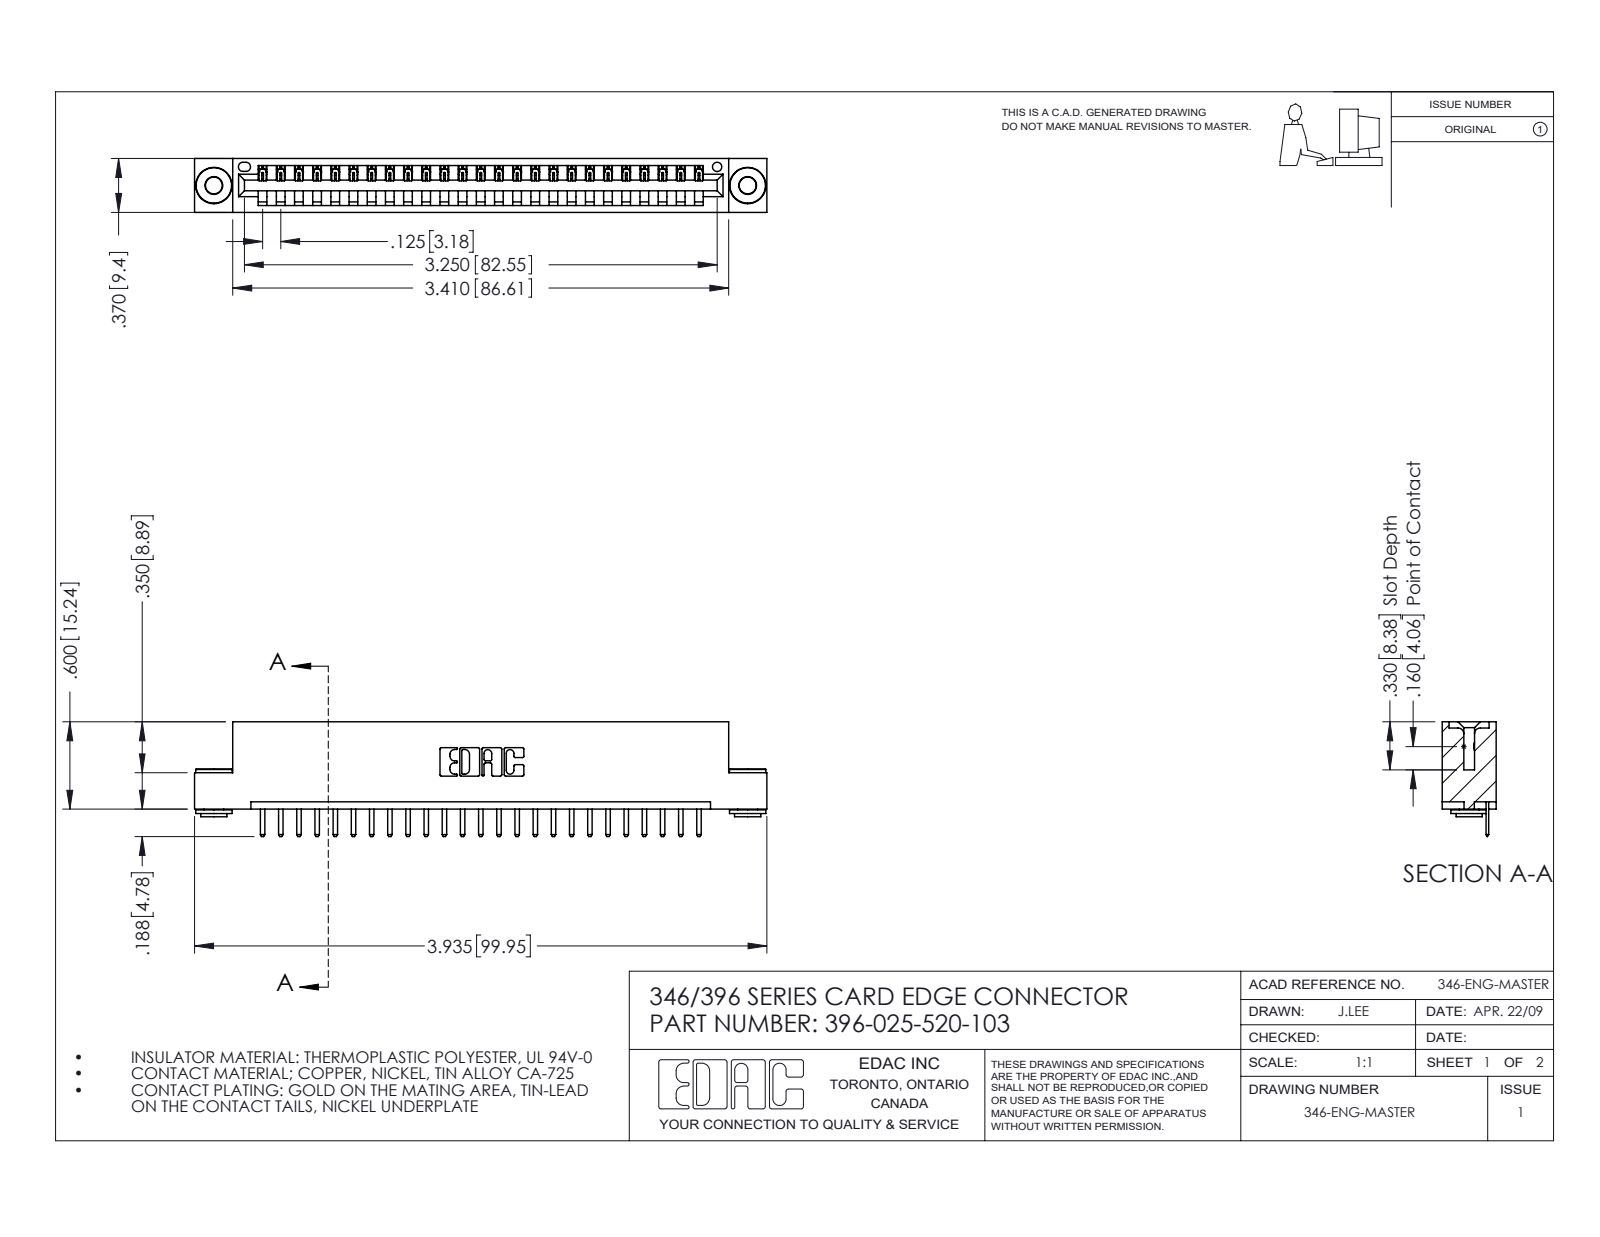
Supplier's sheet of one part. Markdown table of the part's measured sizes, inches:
| quantity | value |
| --- | --- |
| part name | 345-250-002_345-250-002-102; 396-025-520-103; 346 Part_Flush Mounting Lugs - 0.156 Dia-TH; 345-292-001_345-293-120 |
| STEP written by | SolidWorks 2016 (CONFIG_CONTROL_DESIGN) |
| units | inches |
| bodies | 28 solids, 1710 faces (1136 planar, 566 cylindrical, 8 other) |
| overall size | 3.935 × 0.788 × 0.37 |
| volume | 0.573 in³ |
| surface area | 17.89 in² |
| round holes (diameter × count) | 0.116 × 2, 0.156 × 2, 0.064 × 1 |
| round bosses / shafts (diameter × count) | 0.25 × 2, 0.18 × 2, 0.136 × 2 |
| partial cylindrical surfaces (radius × count) | 0.01 × 52, 0.006 × 50, 0.01 × 22, 0.007 × 6, 0.031 × 6, 0.026 × 3, 0.031 × 2, 0.04 × 2 |
| main face-to-face distances | 0.048, 0.322, 0.37, 0.25, 0.148, 0.222, 0.1, 0.174, 0.025, 0.072 |
| hole center spacings | 0.246, 3.462, 3.67 |
